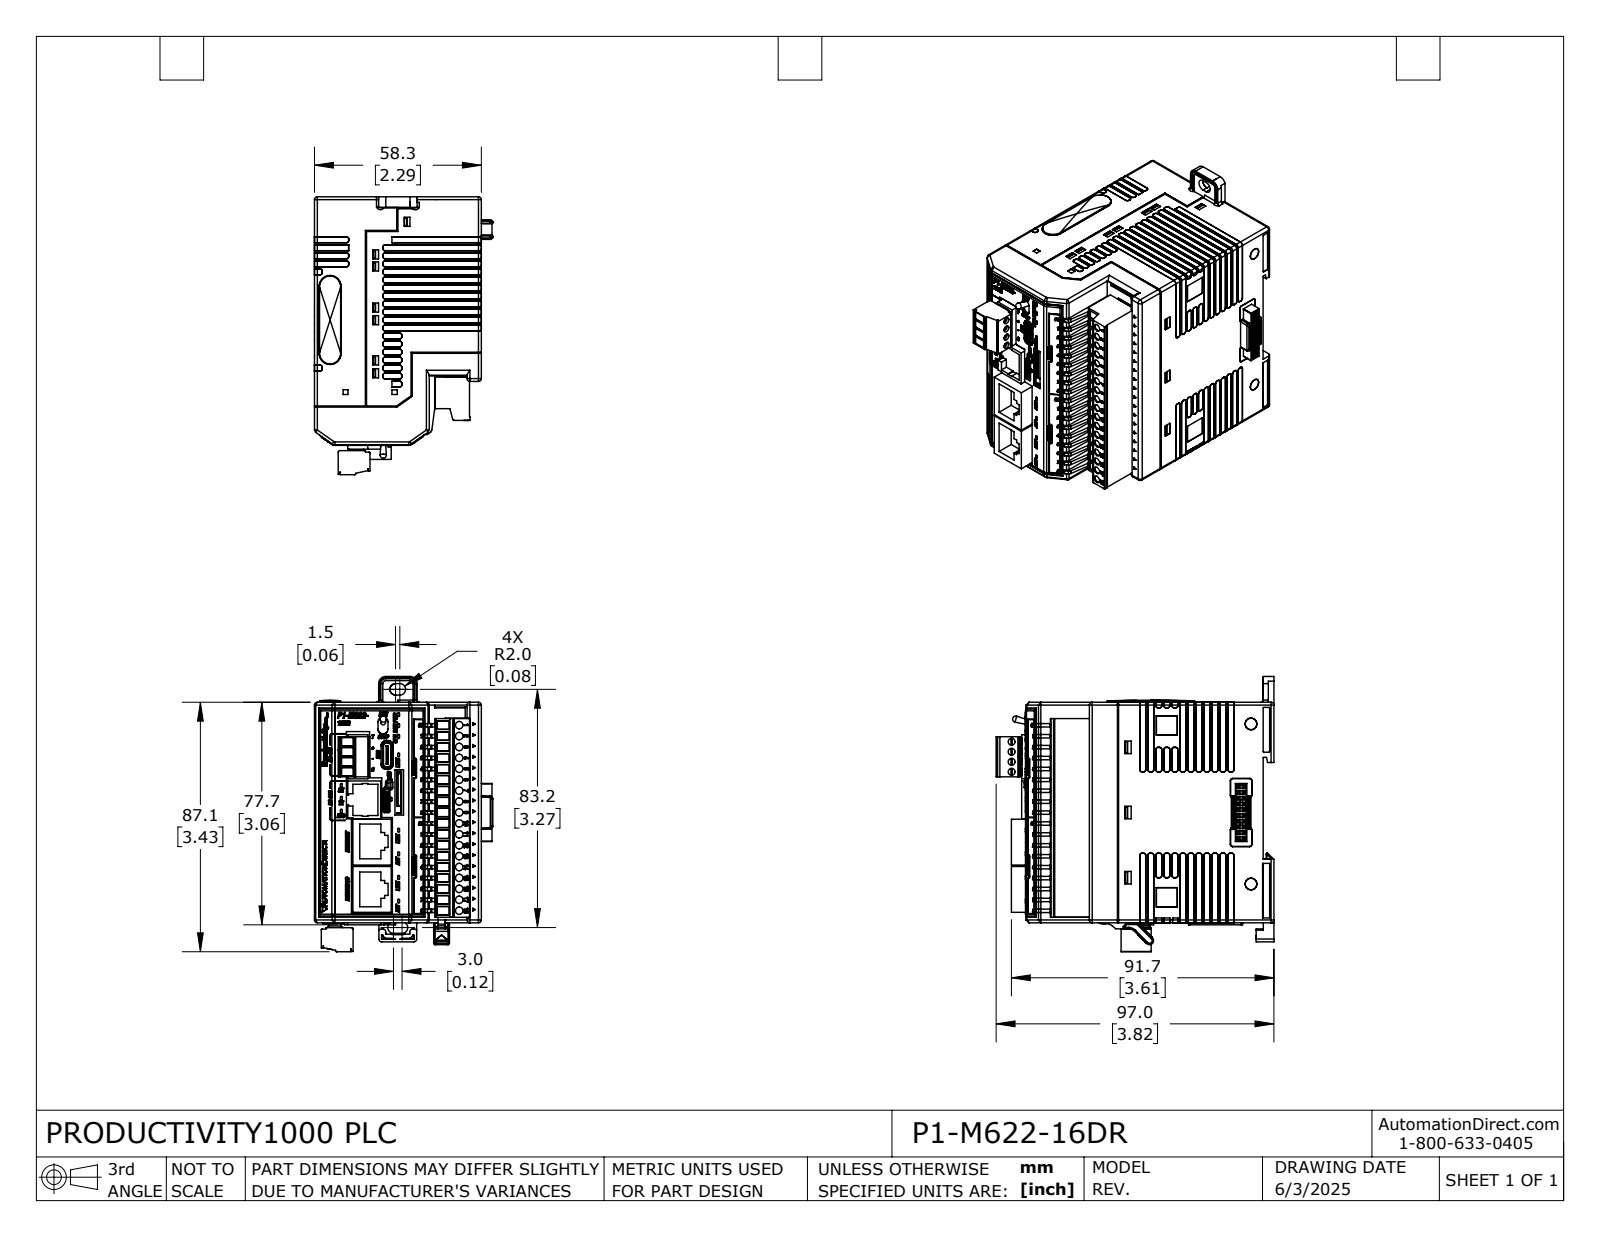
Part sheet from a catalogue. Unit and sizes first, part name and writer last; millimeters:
Units: millimetres
Overall size (bounding box): 93.6 × 91.7 × 62.3
Partial cylindrical surfaces — rounded edges, fillets, slot ends (radius × count): R0.3 ×186, R0.2 ×80, R0.5 ×53, R1 ×33, R2 ×8, R0.6 ×7, R1.5 ×7, R0.3 ×4
Main face-to-face distances: 1.3, 0.5, 56.8, 1, 57.8, 76.5, 76.8, 58.3, 76.7, 77
Volume: 35 360 mm³ · Surface area: 76 320 mm²
Bodies: 12 solids, 3634 faces (2065 planar, 886 cylindrical, 683 other)
Part name (STEP PRODUCT): P1-M622-16DR
STEP written by: SolidWorks 2024 (AUTOMOTIVE_DESIGN)
